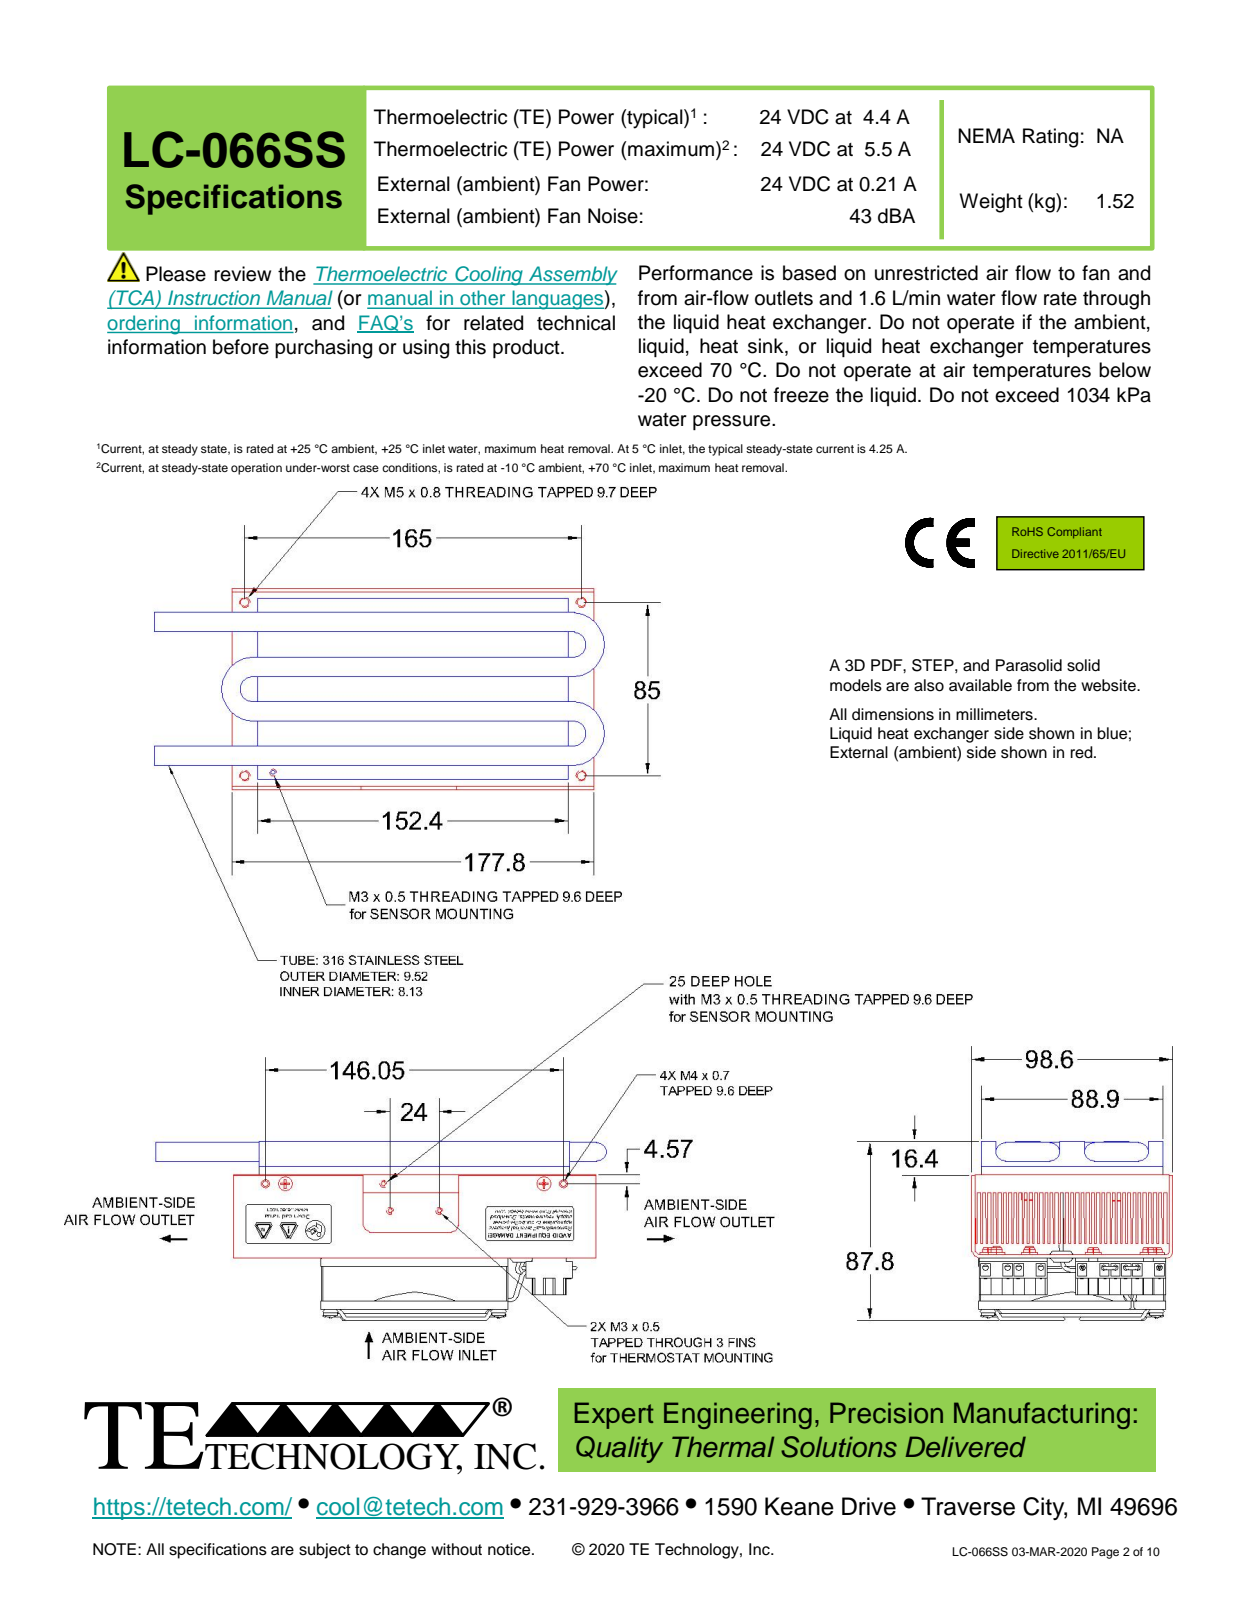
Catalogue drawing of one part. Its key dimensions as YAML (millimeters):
part_name: "dummy 30x30x4.0; 7401 heat sink shroud; PEM LKS 6-32-2; 7401heat sink shroud with pems (+8 more)"
step_written_by: "Alibre (AUTOMOTIVE_DESIGN)"
units: millimeters
bodies: {solids: 124, faces: 3554, planar: 1512, cylindrical: 529, other: 1513}
overall_size: [220.98, 98.48, 87.9]
volume: 584550
surface_area: 623334
round_holes:
  - {diameter: 4, count: 12}
  - {diameter: 2.64, count: 10}
  - {diameter: 2.65, count: 8}
  - {diameter: 5.56, count: 8}
  - {diameter: 3.1, count: 6}
  - {diameter: 4.17, count: 6}
  - {diameter: 4.22, count: 6}
  - {diameter: 4.27, count: 6}
  - {diameter: 4.83, count: 6}
  - {diameter: 5.59, count: 6}
  - {diameter: 6.35, count: 6}
  - {diameter: 11.18, count: 6}
round_bosses_or_shafts:
  - {diameter: 3.51, count: 18}
  - {diameter: 1.42, count: 18}
  - {diameter: 1.83, count: 10}
  - {diameter: 1.8, count: 9}
  - {diameter: 6.86, count: 8}
  - {diameter: 6.34, count: 8}
  - {diameter: 1.8, count: 8}
  - {diameter: 9.53, count: 7}
partial_cylinders:
  - {radius: 1, count: 49}
  - {radius: 0.2, count: 34}
  - {radius: 0.25, count: 16}
  - {radius: 3, count: 12}
  - {radius: 0.5, count: 10}
  - {radius: 0.7, count: 4}
  - {radius: 2.35, count: 4}
  - {radius: 3.75, count: 4}
face_to_face_distances: [4.12, 1.6, 45.01, 40.89, 3.99, 41.02, 12.5, 8.51, 8.38, 32.51]
hole_center_spacings: [10.8, 5.4, 16.2, 5.54, 12.48, 14.72, 27, 10]
